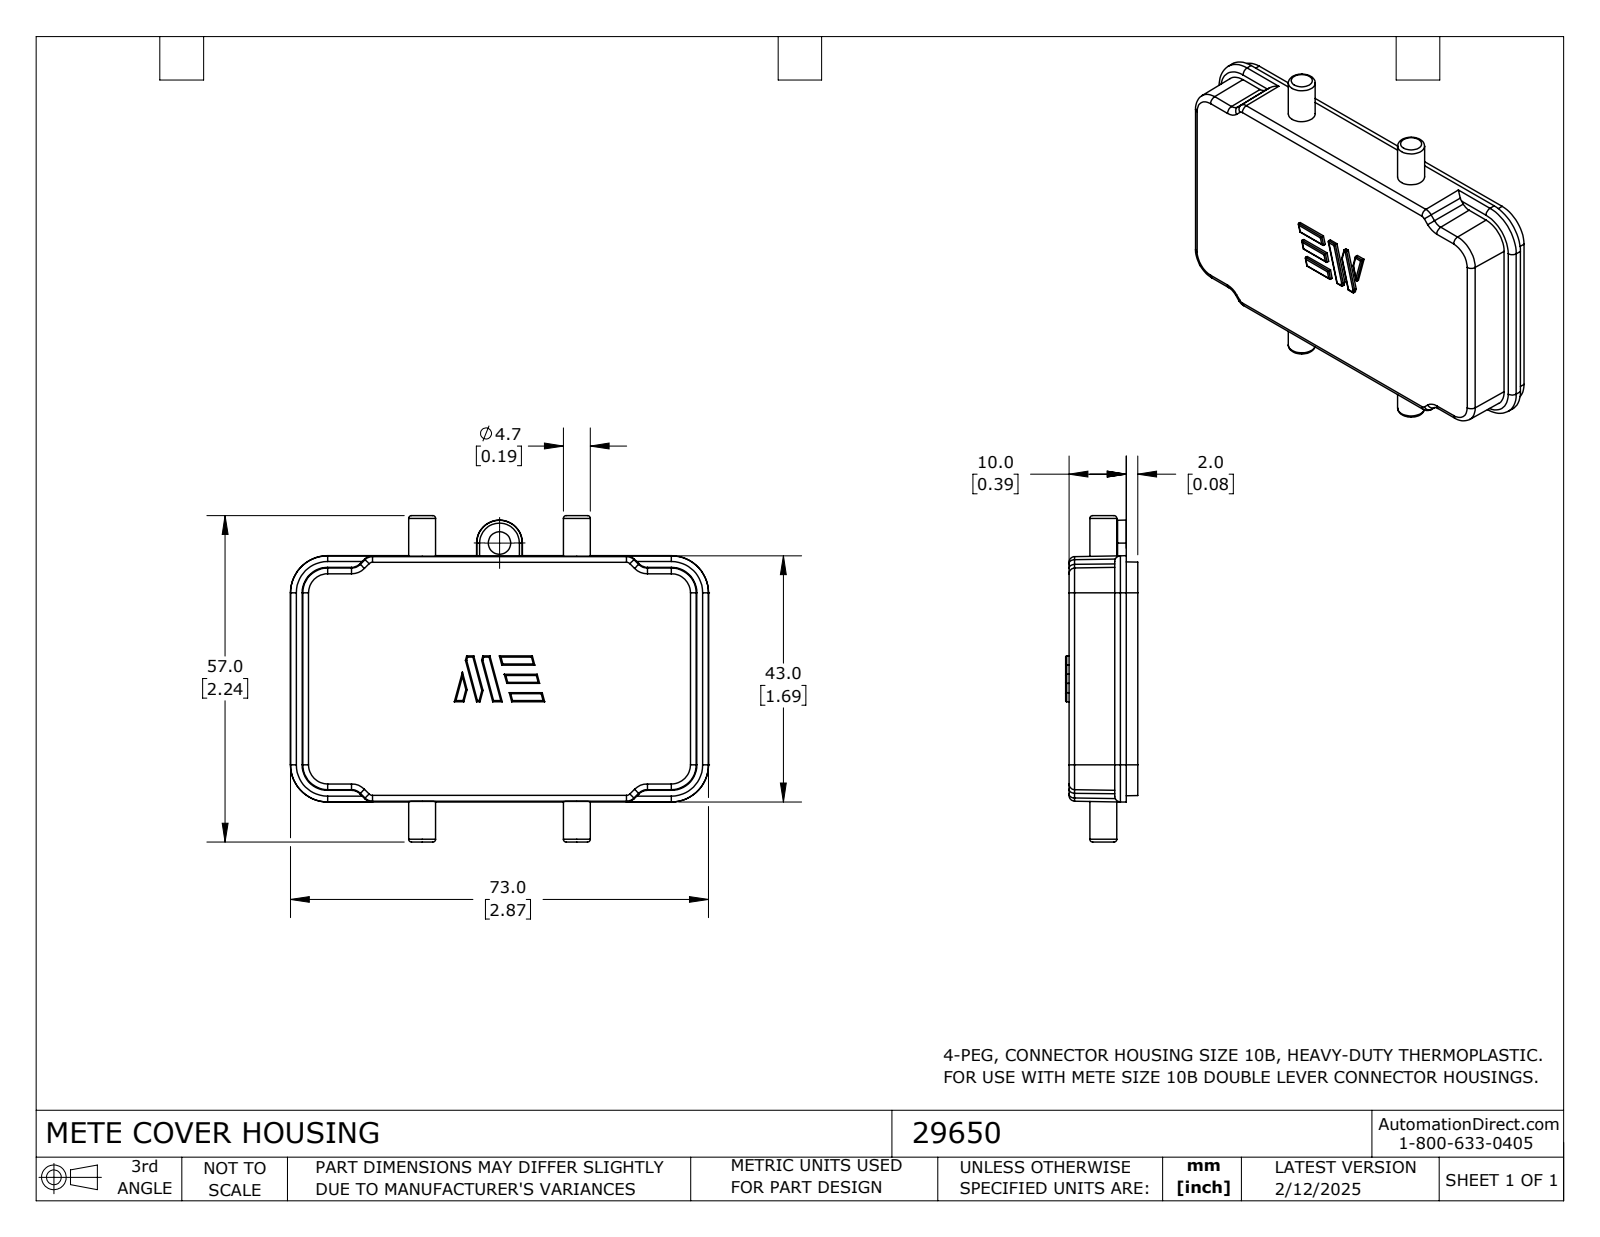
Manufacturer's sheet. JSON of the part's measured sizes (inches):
{"part_name": "29650", "step_written_by": "SolidWorks 2024 (CONFIG_CONTROL_DESIGN)", "units": "inches", "bodies": {"solids": 1, "faces": 223, "planar": 80, "cylindrical": 67, "other": 76}, "overall_size": [2.874, 2.244, 0.496], "volume_in3": 0.657, "surface_area_in2": 17.12, "round_bosses_or_shafts": [[0.185, 2]], "partial_cylinders_radius": [[0.008, 18], [0.039, 14], [0.02, 12]], "face_to_face_distances": [0.079, 0.102, 0.394, 0.067, 0.315, 0.043, 0.472, 0.024, 0.146, 1.65]}
